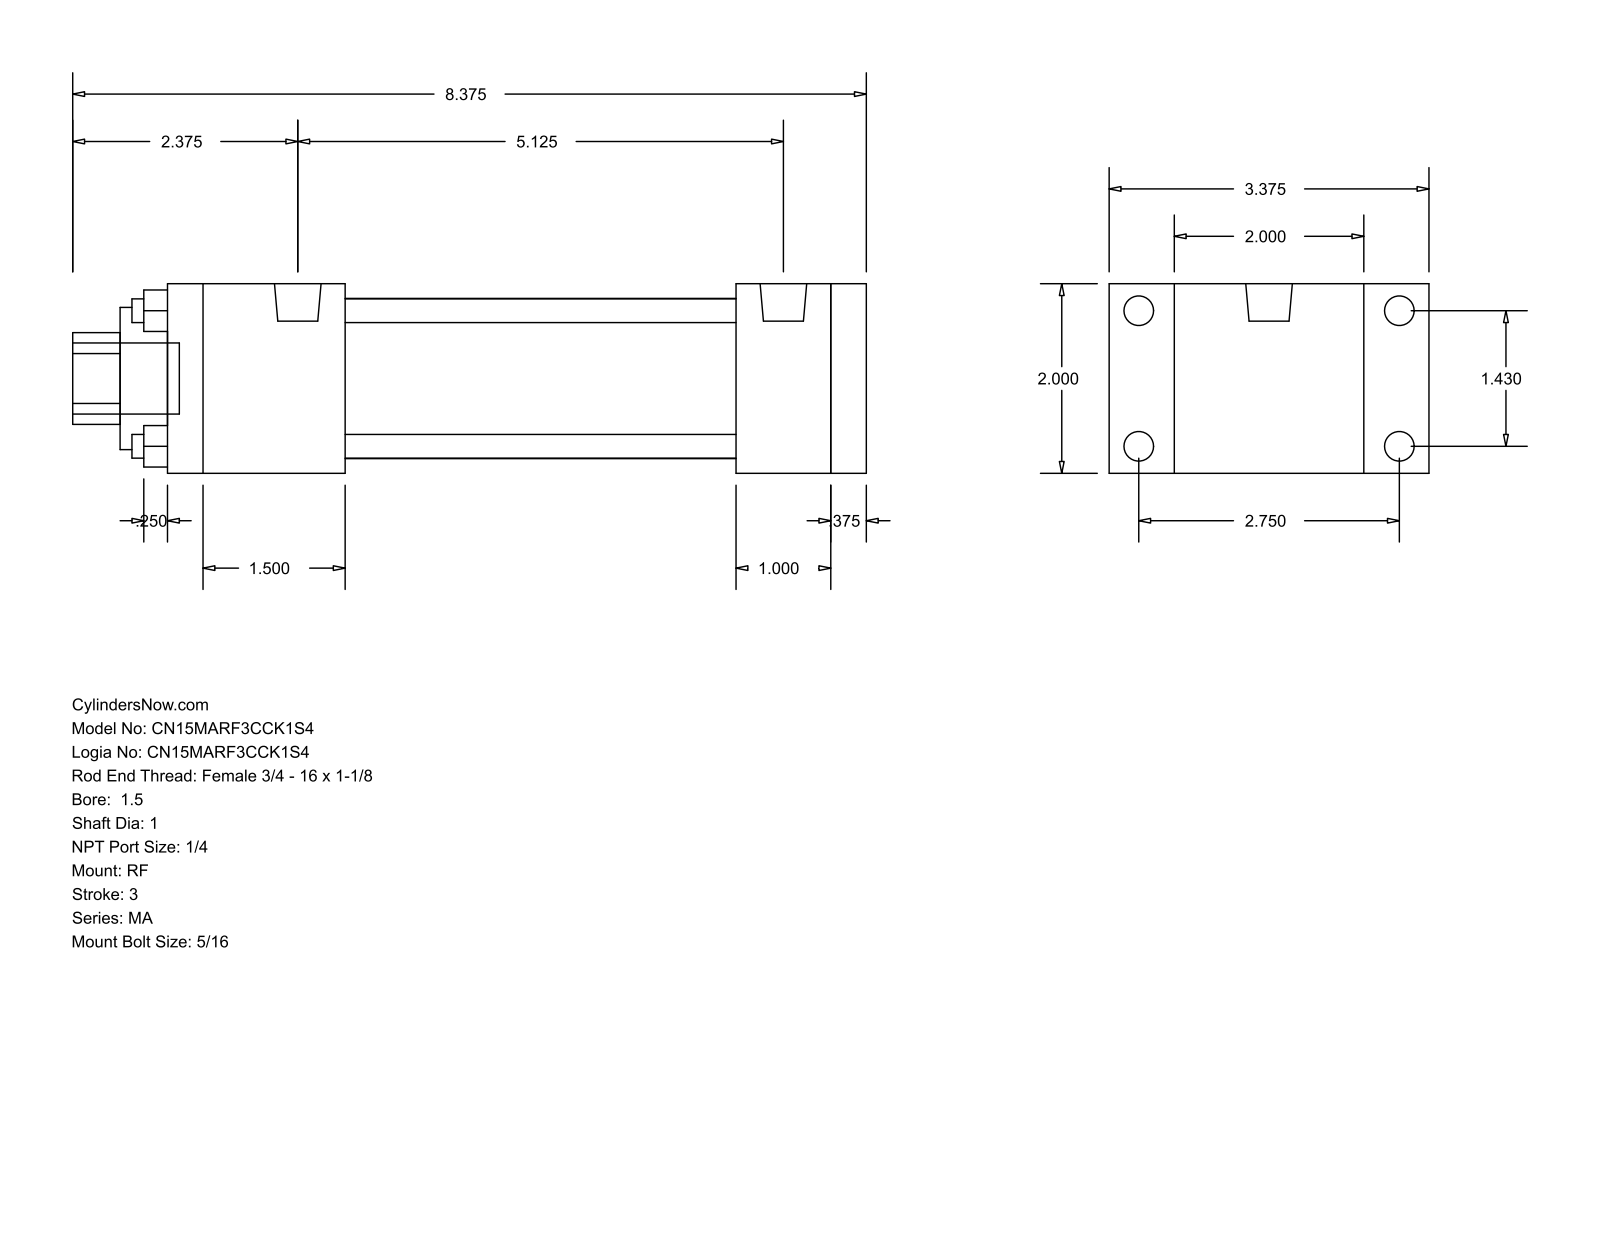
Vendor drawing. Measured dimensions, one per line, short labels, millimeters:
name: MA_RF__0150_1
written by: GSSL Pune (CONFIG_CONTROL_DESIGN)
unit: mm
bodies: 0 solids, 92 faces (64 planar, 28 cylindrical, 0 other)
size: 212.72 × 85.72 × 50.8
holes: 4× ⌀6.35, 1× ⌀25.4, 1× ⌀38.1, 1× ⌀42.93
bosses: 8× ⌀7.94, 2× ⌀12.49, 1× ⌀19.05
rounds: 1× R12.29
face distances: 50.8, 9.52, 187.32, 177.8, 25.4, 152.4, 34.92, 47.63, 104.77, 130.17
hole spacings: 25.68, 36.32, 51.36
